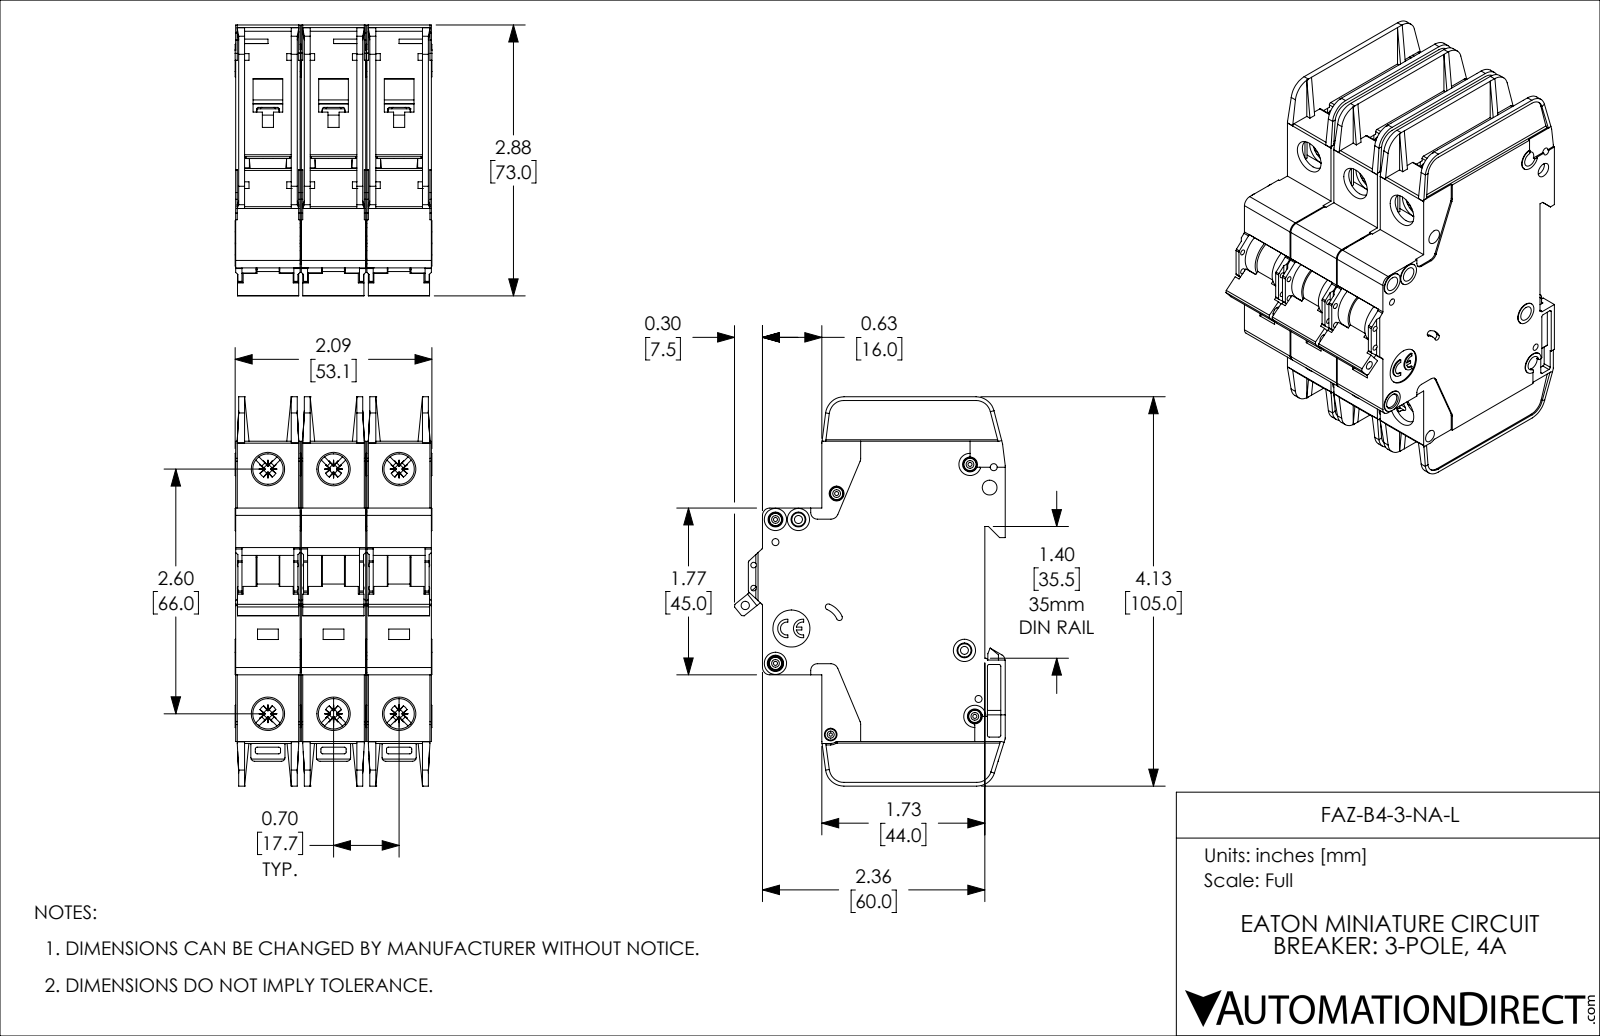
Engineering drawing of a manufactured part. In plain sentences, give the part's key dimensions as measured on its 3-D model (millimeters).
The part is named "FAZ-B4-3-NA-L". Its 3-D file was written by "SolidWorks 2019 (AUTOMOTIVE_DESIGN)". It is 3 solids with 3381 faces: 2013 planar, 1071 cylindrical and 297 other. Overall it measures 105 by 73.1 by 53.1 millimeters. Its volume is 230 200 cubic millimeters and its surface area 79 350 square millimeters. Round holes: 8 of diameter 4, 6 of diameter 8.2, 5 of diameter 1.1, 4 of diameter 1.9, 2 of diameter 1.5, 2 of diameter 2.2, 1 of diameter 0.9, 1 of diameter 2.3, 1 of diameter 2.5, 1 of diameter 3.4, 1 of diameter 10. Round bosses or shafts: 5 of diameter 3.3, 4 of diameter 6, 4 of diameter 3, 3 of diameter 2.5. Partial cylindrical surfaces (rounded edges, fillets, slot ends): 72 of radius 0.5, 30 of radius 0.4, 18 of radius 1, 12 of radius 1.1, 12 of radius 2, 6 of radius 0.2, 6 of radius 0.3, 6 of radius 0.7. The main face-to-face distances are 17.7, 1.2, 35.4, 17.4, 15, 35.1, 18.9, 16.5, 2.7, 2.4. The hole center spacings are 17.7, 68.3, 66, 6.2, 13.6, 22.1, 35.4, 74.9.
